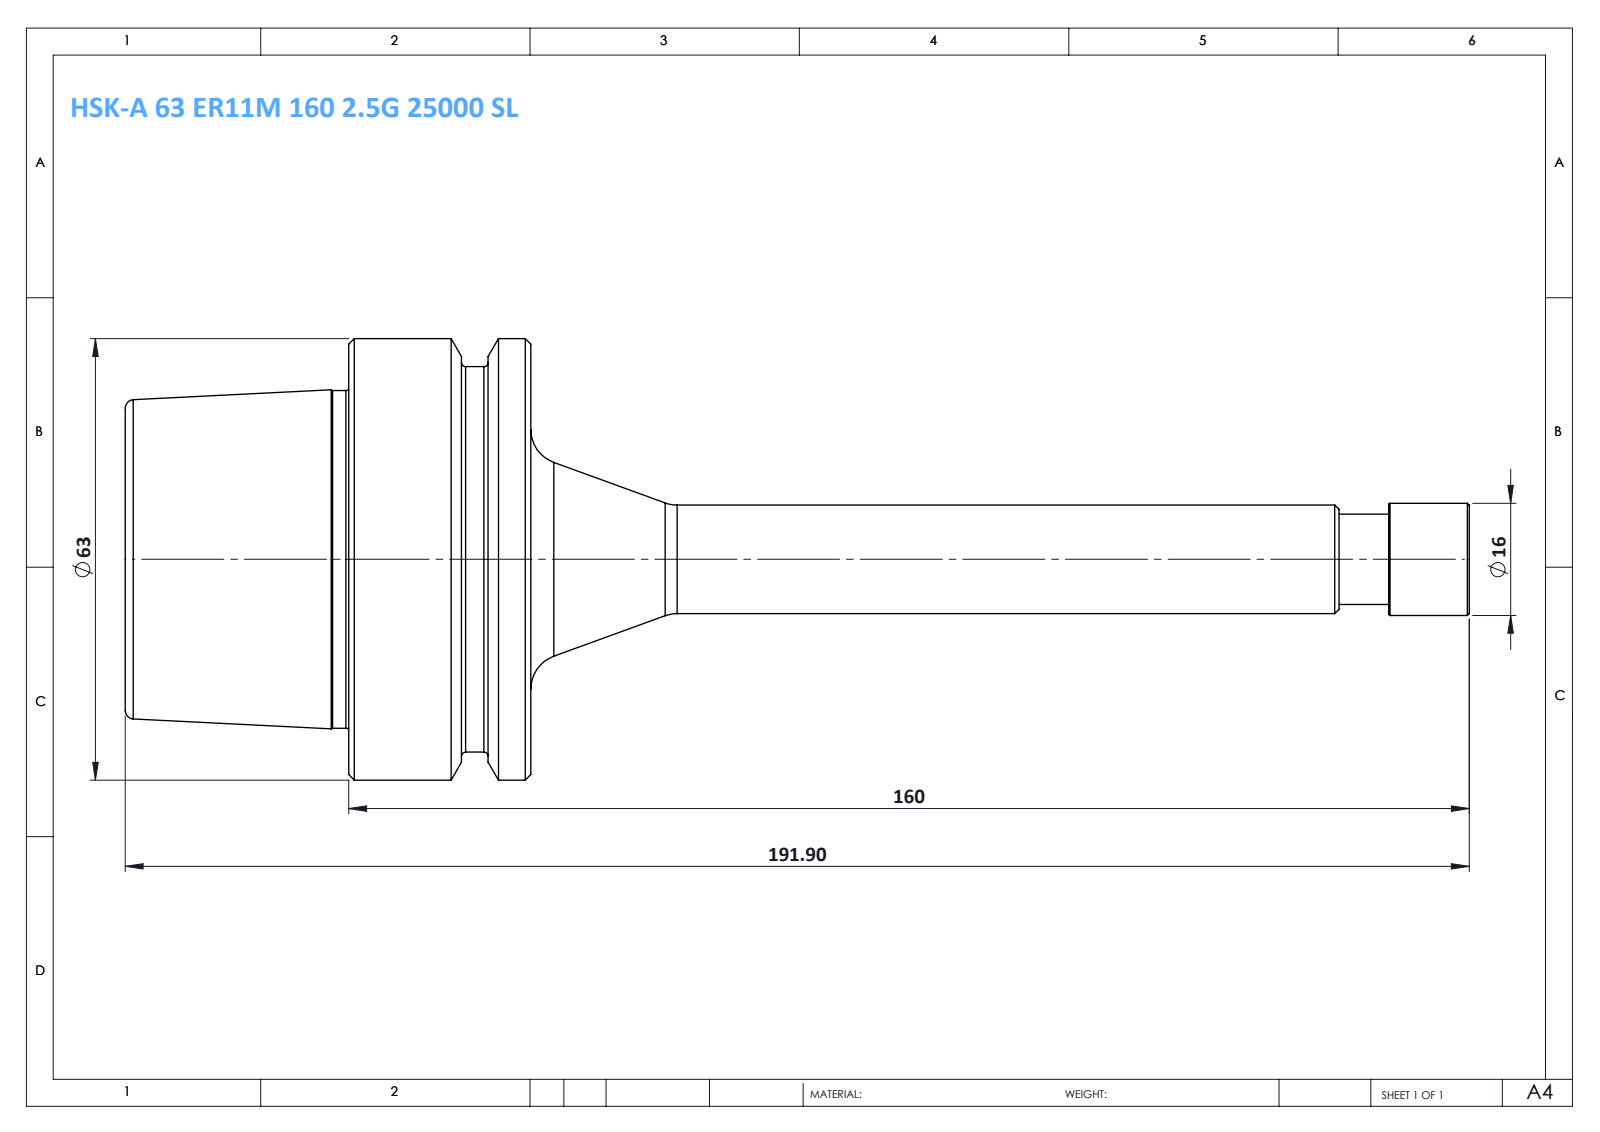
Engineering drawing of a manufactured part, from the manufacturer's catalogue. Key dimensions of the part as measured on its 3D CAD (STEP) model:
Part name (STEP PRODUCT): HSK-A 63ER11M 160 2.5G 25000 SL
STEP written by: SolidWorks 2014 (CONFIG_CONTROL_DESIGN)
Units: millimetres
Bodies: 1 solid, 56 faces (8 planar, 14 cylindrical, 34 other)
Overall size (bounding box): 191.9 × 63 × 63
Volume: 162 627 mm³ · Surface area: 23 049 mm²
Round bosses / shafts (diameter × count): ⌀63 ×1, ⌀55 ×1, ⌀48.2 ×1, ⌀16 ×1, ⌀15.5 ×1, ⌀12.9 ×1
Main face-to-face distances: 57.9, 26, 31.9, 134, 160, 191.9, 140.1, 6.1, 19.9, 51.8
